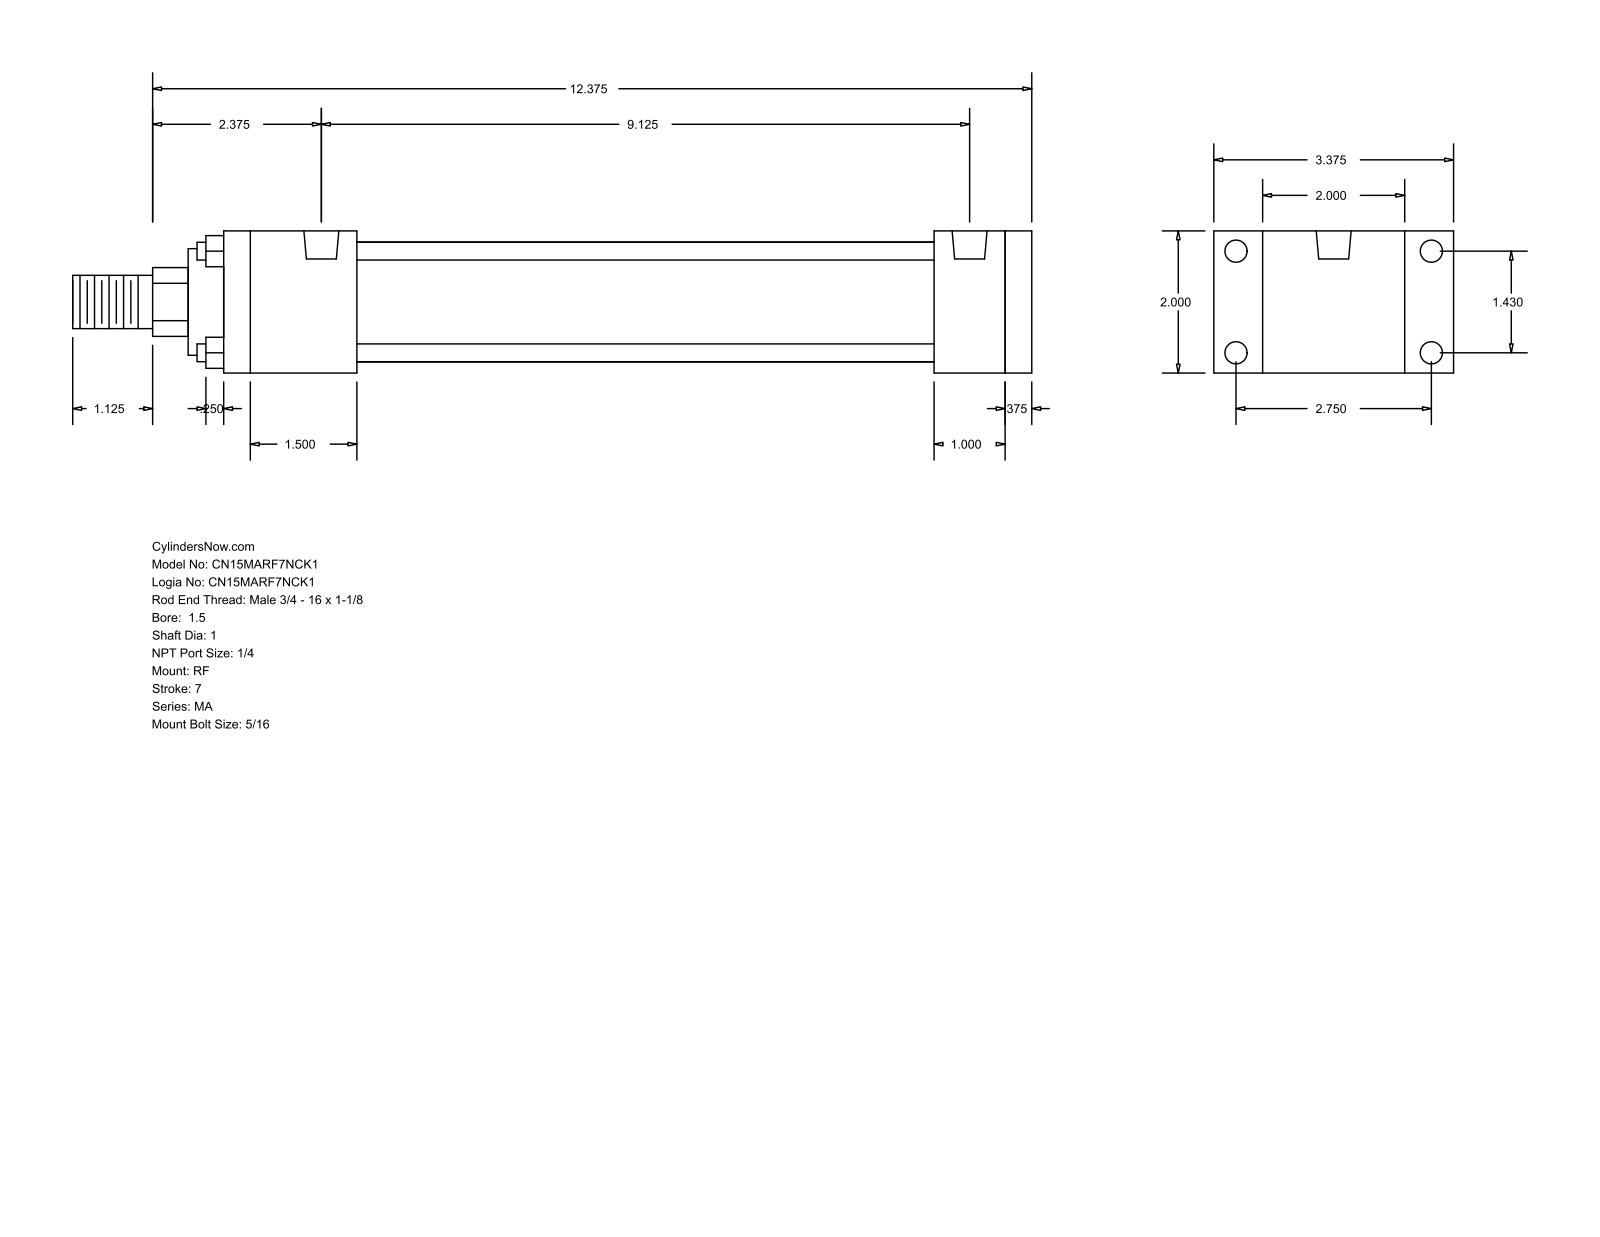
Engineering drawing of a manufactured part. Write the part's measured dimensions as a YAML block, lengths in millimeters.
part_name: "MA_RF__0150_1"
step_written_by: "GSSL Pune (CONFIG_CONTROL_DESIGN)"
units: millimeters
bodies: {solids: 0, faces: 92, planar: 64, cylindrical: 28, other: 0}
overall_size: [342.9, 85.72, 50.8]
round_holes:
  - {diameter: 7.94, count: 8}
  - {diameter: 12.49, count: 2}
round_bosses_or_shafts:
  - {diameter: 6.35, count: 4}
  - {diameter: 42.93, count: 1}
  - {diameter: 38.1, count: 1}
  - {diameter: 25.4, count: 1}
  - {diameter: 19.05, count: 1}
partial_cylinders:
  - {radius: 12.29, count: 1}
face_to_face_distances: [50.8, 9.52, 288.92, 279.4, 25.4, 254, 34.92, 47.63, 206.37, 231.77]
hole_center_spacings: [36.32, 69.84, 78.72, 231.77]
